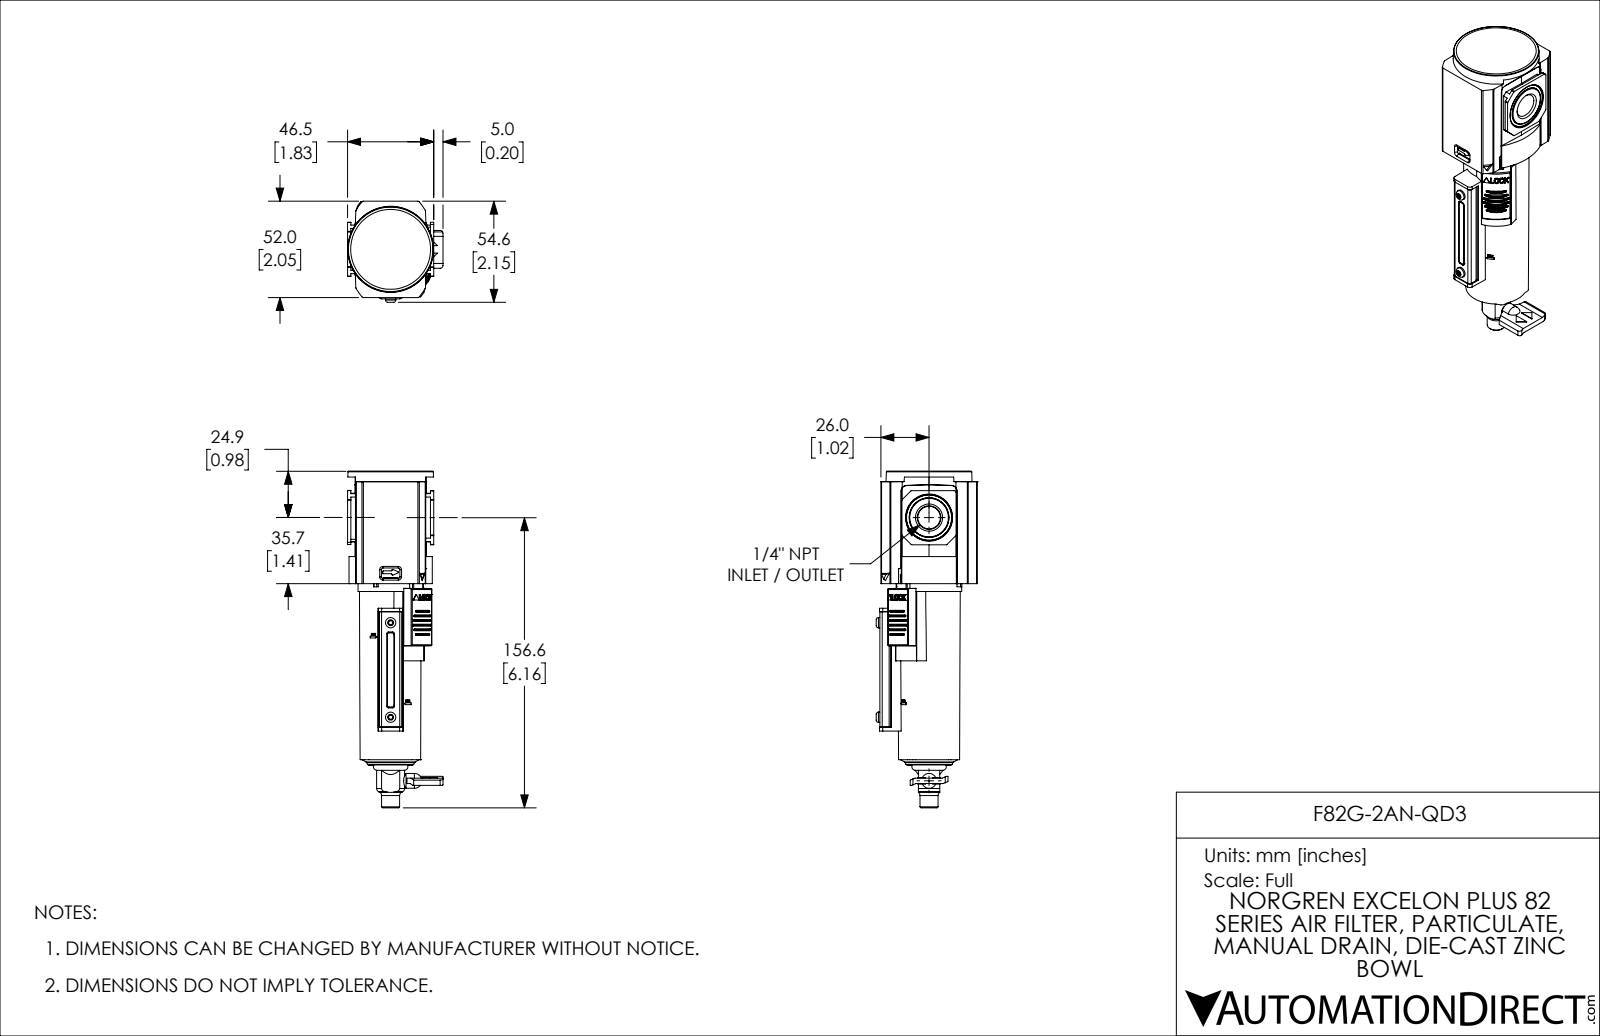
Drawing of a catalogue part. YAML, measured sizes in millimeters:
part_name: "F82G-2AN-QD3"
step_written_by: "SolidWorks 2021 (CONFIG_CONTROL_DESIGN)"
units: millimeters
bodies: {solids: 5, faces: 1127, planar: 498, cylindrical: 416, other: 213}
overall_size: [181.6, 54.6, 51.5]
volume: 211600
surface_area: 59190
round_holes:
  - {diameter: 3.3, count: 2}
  - {diameter: 6.4, count: 1}
  - {diameter: 16, count: 1}
round_bosses_or_shafts:
  - {diameter: 5.5, count: 2}
  - {diameter: 35.3, count: 1}
  - {diameter: 34.4, count: 1}
  - {diameter: 32.8, count: 1}
  - {diameter: 31.9, count: 1}
  - {diameter: 23, count: 1}
  - {diameter: 15.9, count: 1}
  - {diameter: 9.7, count: 1}
partial_cylinders:
  - {radius: 0.5, count: 54}
  - {radius: 1, count: 45}
  - {radius: 0.3, count: 12}
  - {radius: 0.5, count: 12}
  - {radius: 0.3, count: 10}
  - {radius: 0.8, count: 8}
  - {radius: 0.9, count: 8}
  - {radius: 1.2, count: 8}
face_to_face_distances: [1.5, 50.5, 37.3, 52, 49, 1.5, 53.2, 54.6, 4.6, 6]
hole_center_spacings: [15.1, 30.2]
